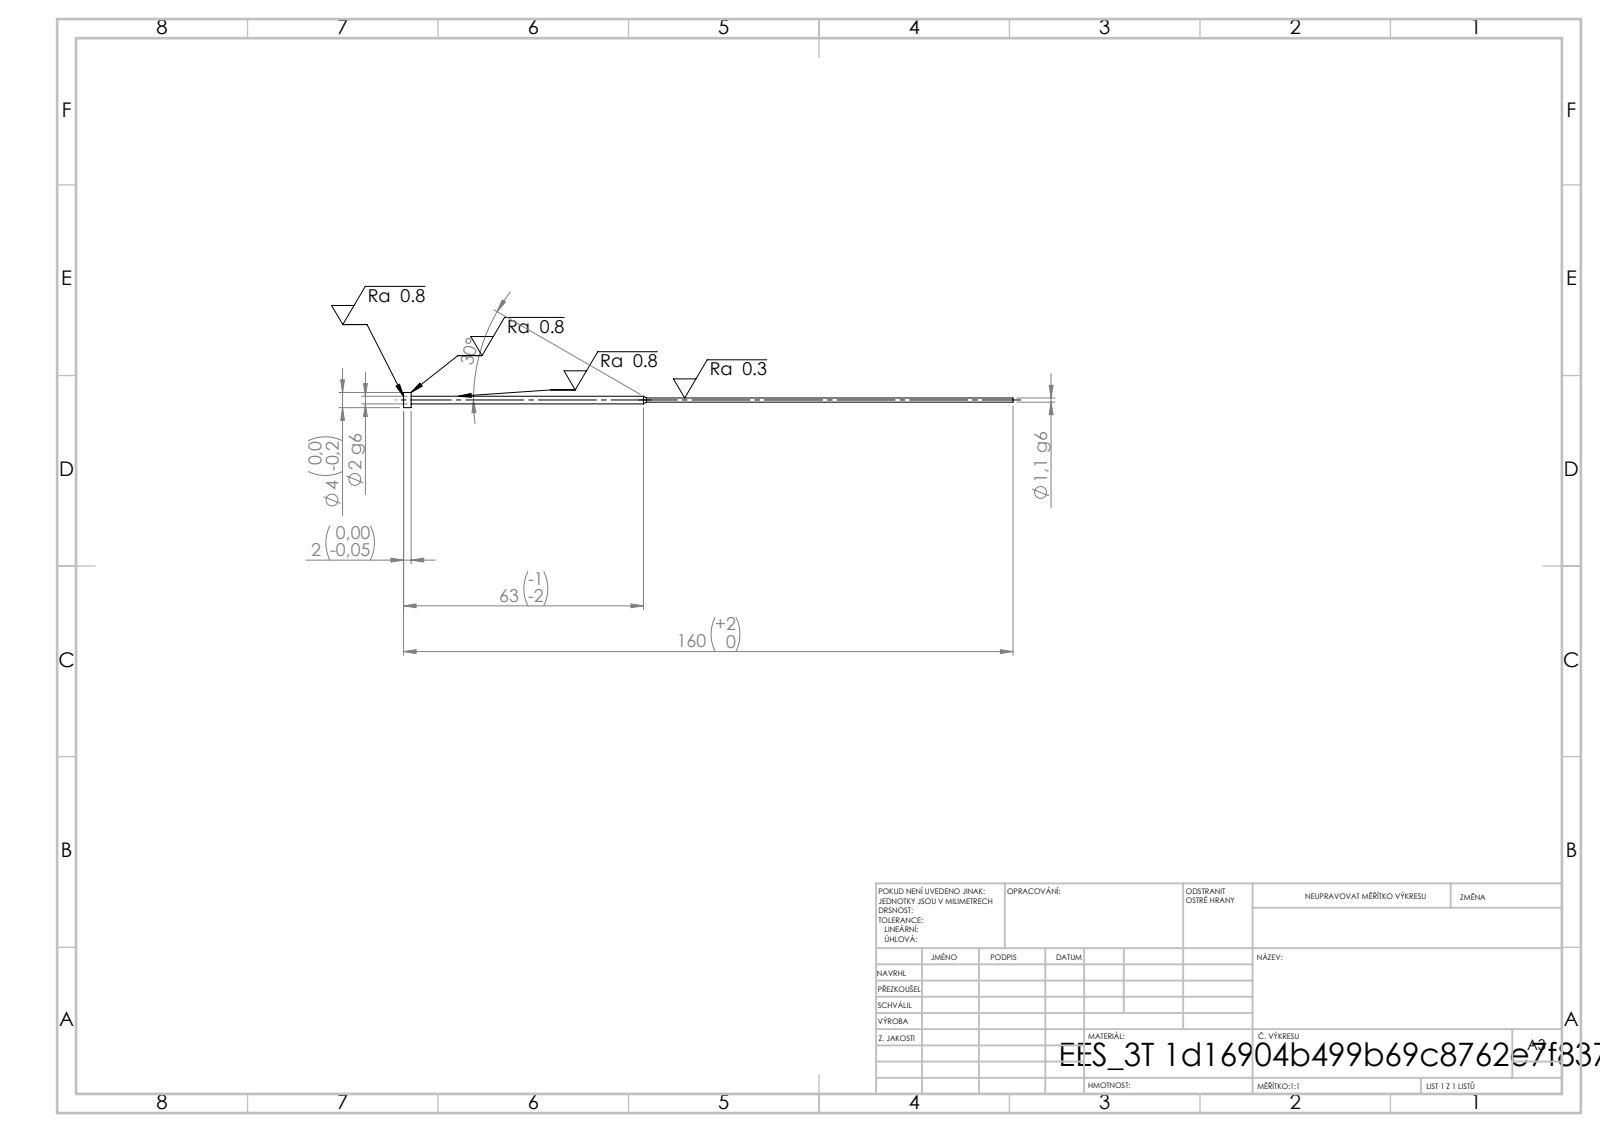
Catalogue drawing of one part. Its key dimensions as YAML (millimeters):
step_written_by: "SolidWorks 2019 (CONFIG_CONTROL_DESIGN)"
units: millimeters
bodies: {solids: 1, faces: 11, planar: 3, cylindrical: 6, other: 2}
overall_size: [160, 4, 4]
volume: 310
surface_area: 768
round_bosses_or_shafts:
  - {diameter: 4, count: 1}
  - {diameter: 2, count: 1}
  - {diameter: 1.1, count: 1}
face_to_face_distances: [2, 158, 160]
